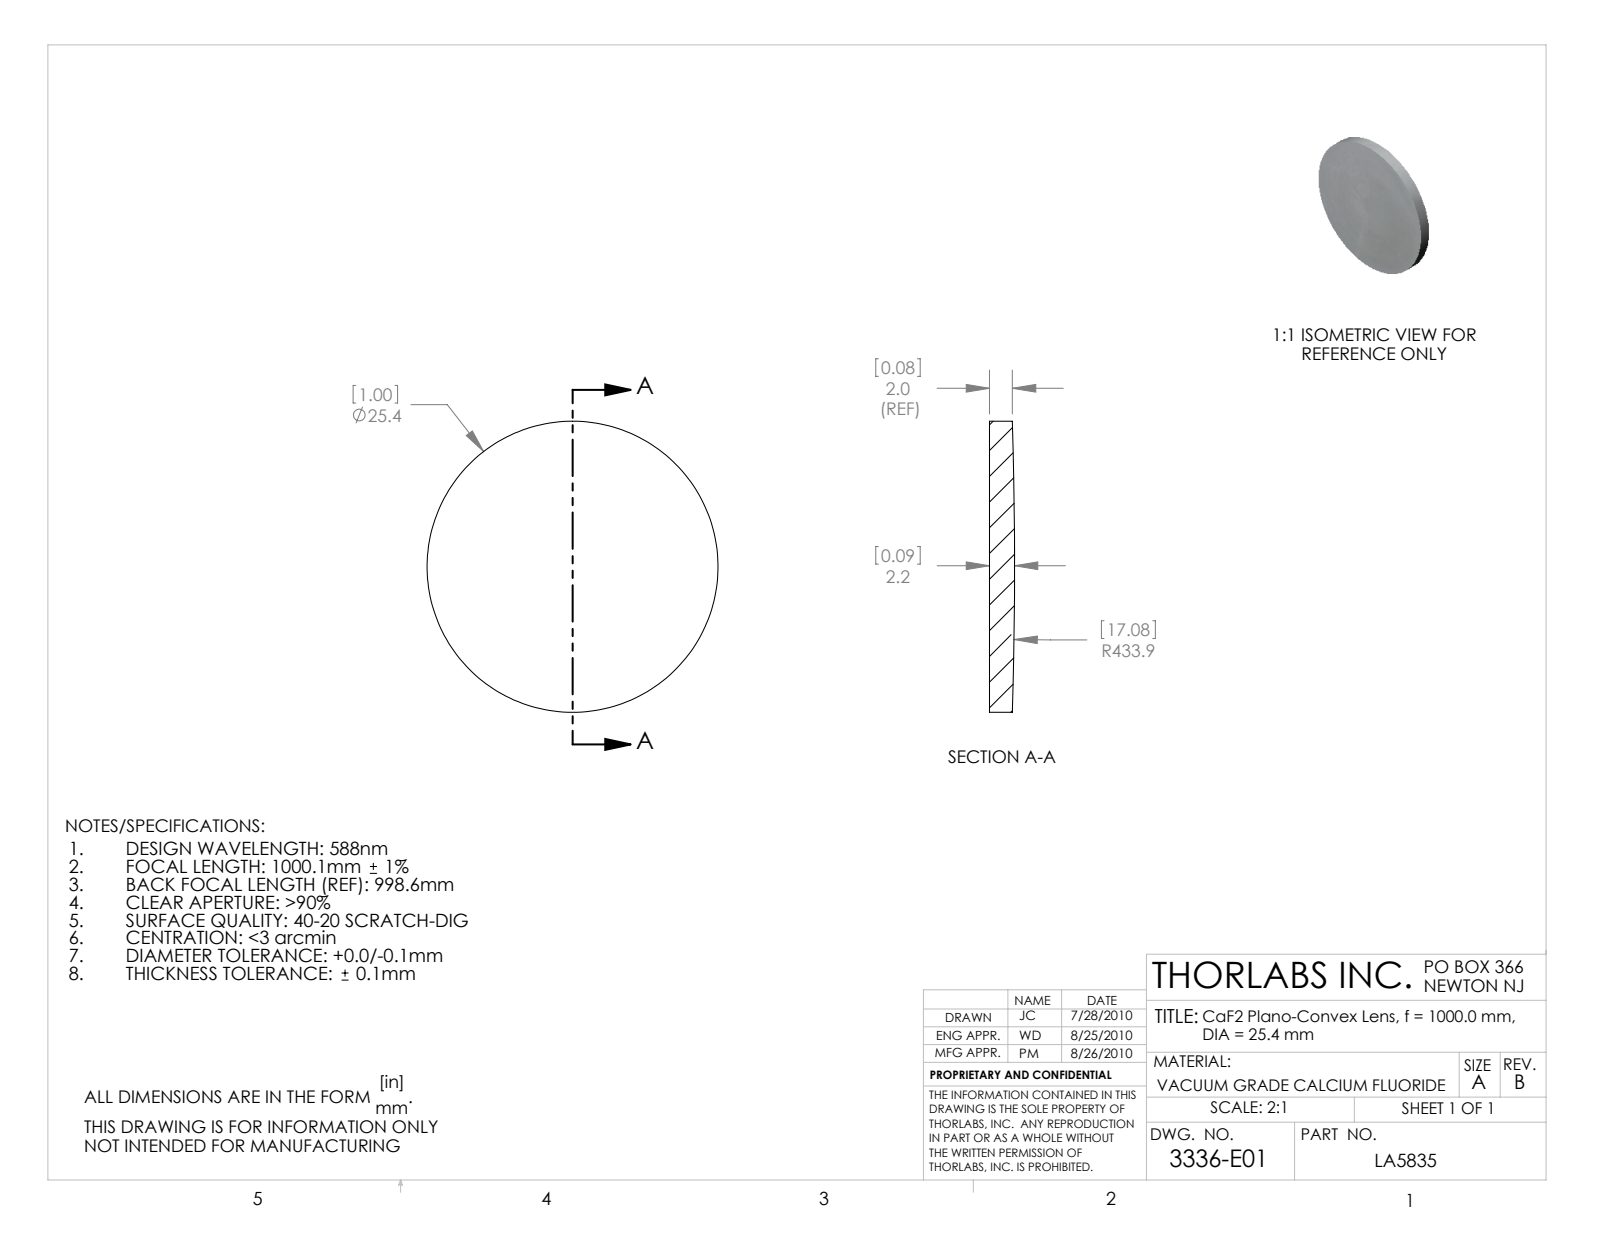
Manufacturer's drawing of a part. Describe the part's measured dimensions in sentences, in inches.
The part is named "3336-E0W". Its 3-D file was written by "SolidWorks 2009 (AUTOMOTIVE_DESIGN)". It is 1 solid with 5 faces: 1 planar, 2 cylindrical and 2 other. Overall it measures 1 by 1 by 0.086 inches. Its volume is 0.065 cubic inches and its surface area 1.818 square inches. Round bosses or shafts: 1 of diameter 1.
